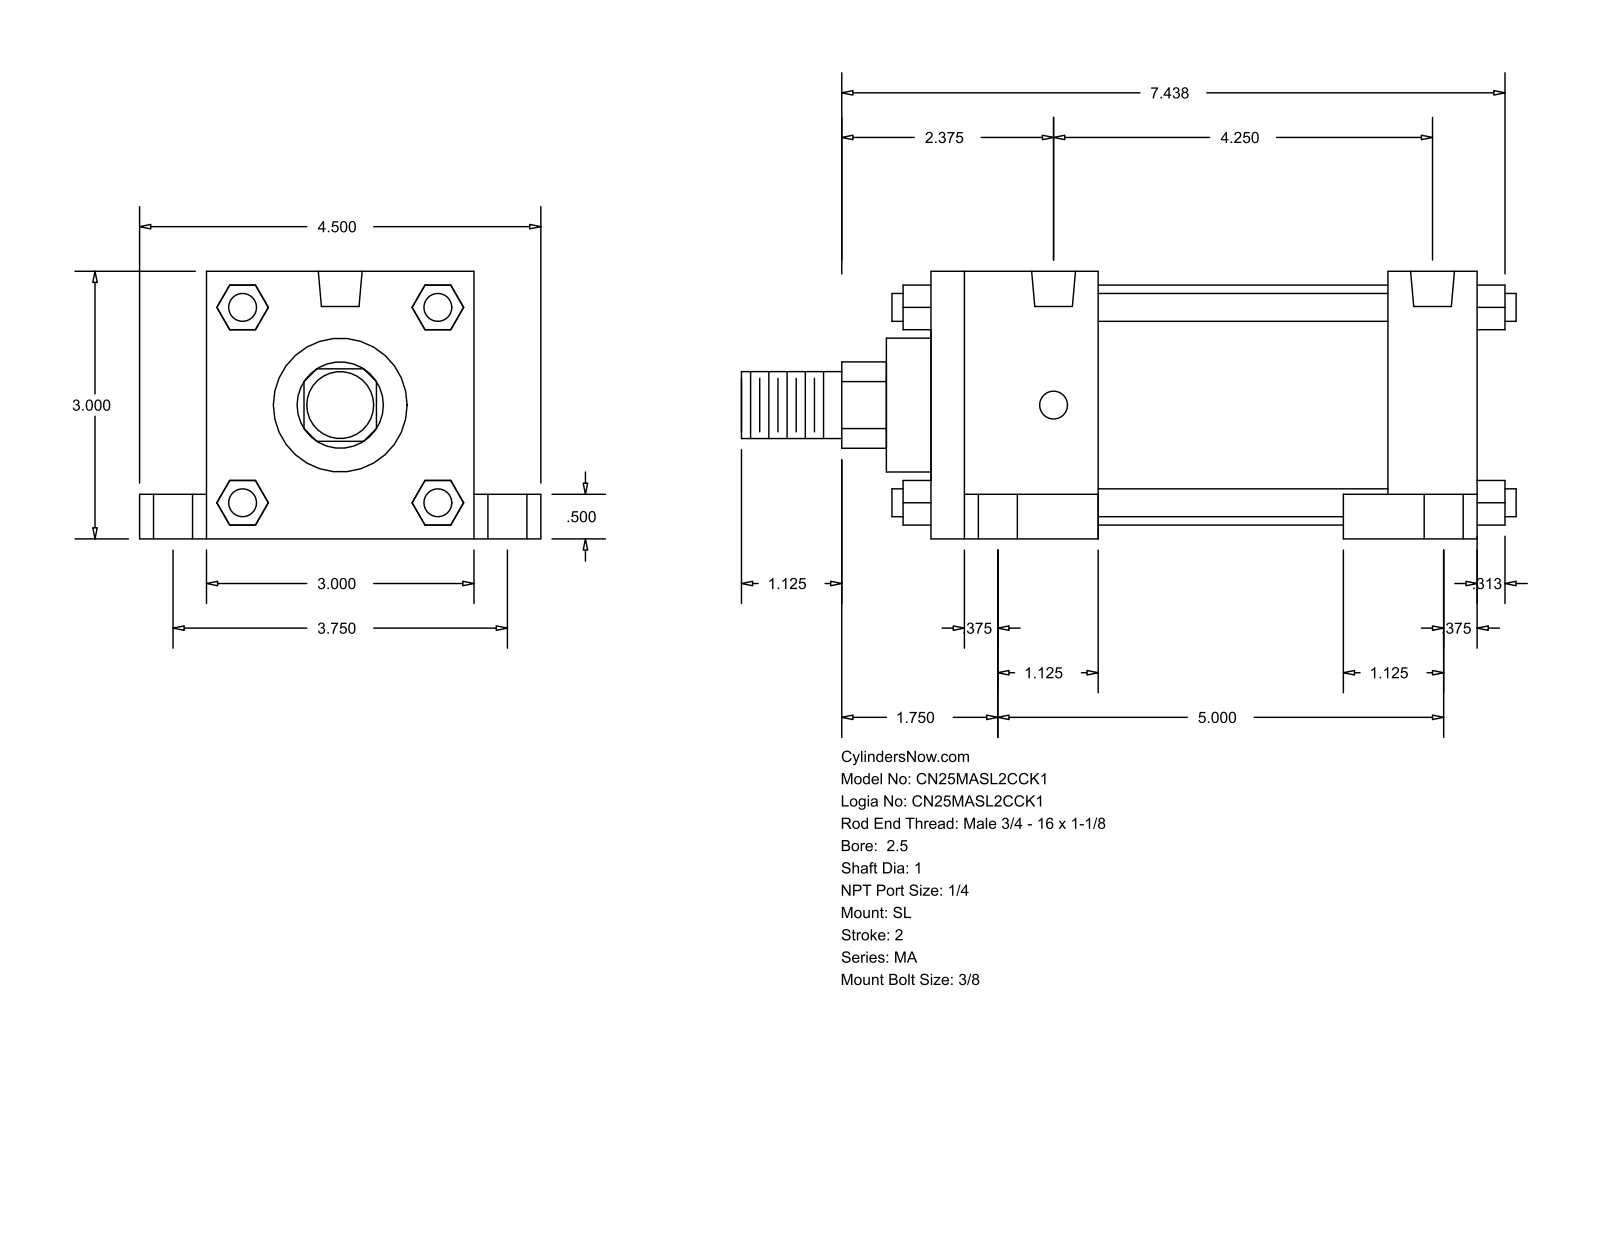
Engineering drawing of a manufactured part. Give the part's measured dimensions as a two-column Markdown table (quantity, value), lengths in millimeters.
| quantity | value |
| --- | --- |
| part name | MA_SL__0250_1 |
| STEP written by | GSSL Pune (CONFIG_CONTROL_DESIGN) |
| units | millimeters |
| bodies | 0 solids, 148 faces (112 planar, 36 cylindrical, 0 other) |
| overall size | 220.66 × 114.3 × 76.2 |
| round holes (diameter × count) | 7.94 × 4, 11.11 × 4, 17.46 × 4, 12.49 × 2 |
| round bosses / shafts (diameter × count) | 7.94 × 4, 68.33 × 1, 38.1 × 1, 25.4 × 1, 19.05 × 1 |
| partial cylindrical surfaces (radius × count) | 12.29 × 1 |
| main face-to-face distances | 76.2, 155.57, 12.7, 25.4, 47.63, 107.94, 130.17, 82.54, 19.05, 95.25 |
| hole center spacings | 47.73, 50.2, 95.24, 107.95, 120.89, 127, 132.67, 158.74 |
